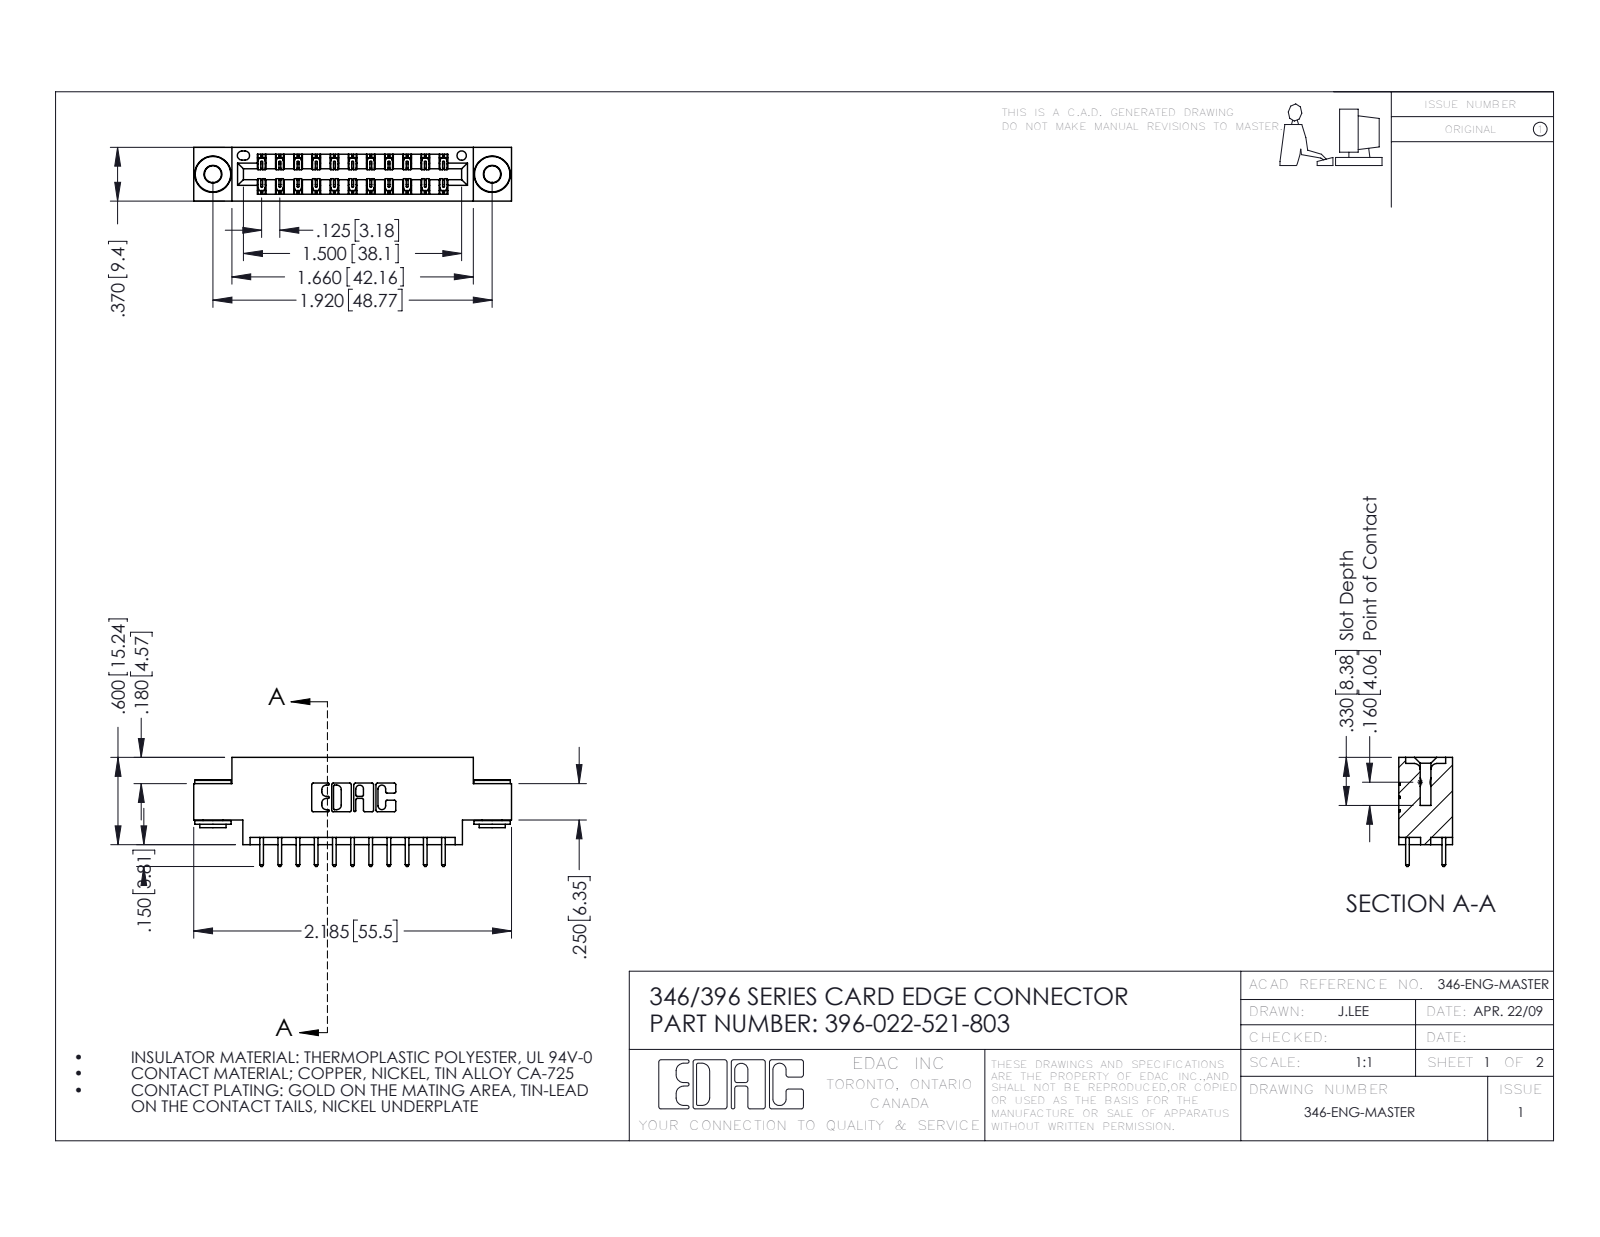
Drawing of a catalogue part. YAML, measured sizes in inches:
part_name: "345-292-001_345-293-121; 396-022-521-803; 345-250-002_345-250-002-102; 346 Part_0.170 Offset - 0.156 Dia-TH"
step_written_by: "SolidWorks 2016 (CONFIG_CONTROL_DESIGN)"
units: inches
bodies: {solids: 25, faces: 1308, planar: 860, cylindrical: 440, other: 8}
overall_size: [2.185, 0.75, 0.37]
volume: 0.307
surface_area: 10.47
round_holes:
  - {diameter: 0.116, count: 2}
  - {diameter: 0.156, count: 2}
  - {diameter: 0.064, count: 1}
round_bosses_or_shafts:
  - {diameter: 0.25, count: 2}
  - {diameter: 0.18, count: 2}
  - {diameter: 0.136, count: 2}
partial_cylinders:
  - {radius: 0.006, count: 33}
  - {radius: 0.01, count: 22}
  - {radius: 0.01, count: 22}
  - {radius: 0.007, count: 6}
  - {radius: 0.031, count: 6}
  - {radius: 0.026, count: 3}
  - {radius: 0.014, count: 2}
  - {radius: 0.022, count: 2}
face_to_face_distances: [0.25, 0.37, 0.048, 0.322, 0.025, 0.275, 0.072, 0.298, 0.148, 0.222]
hole_center_spacings: [0.246, 1.715, 1.92]
